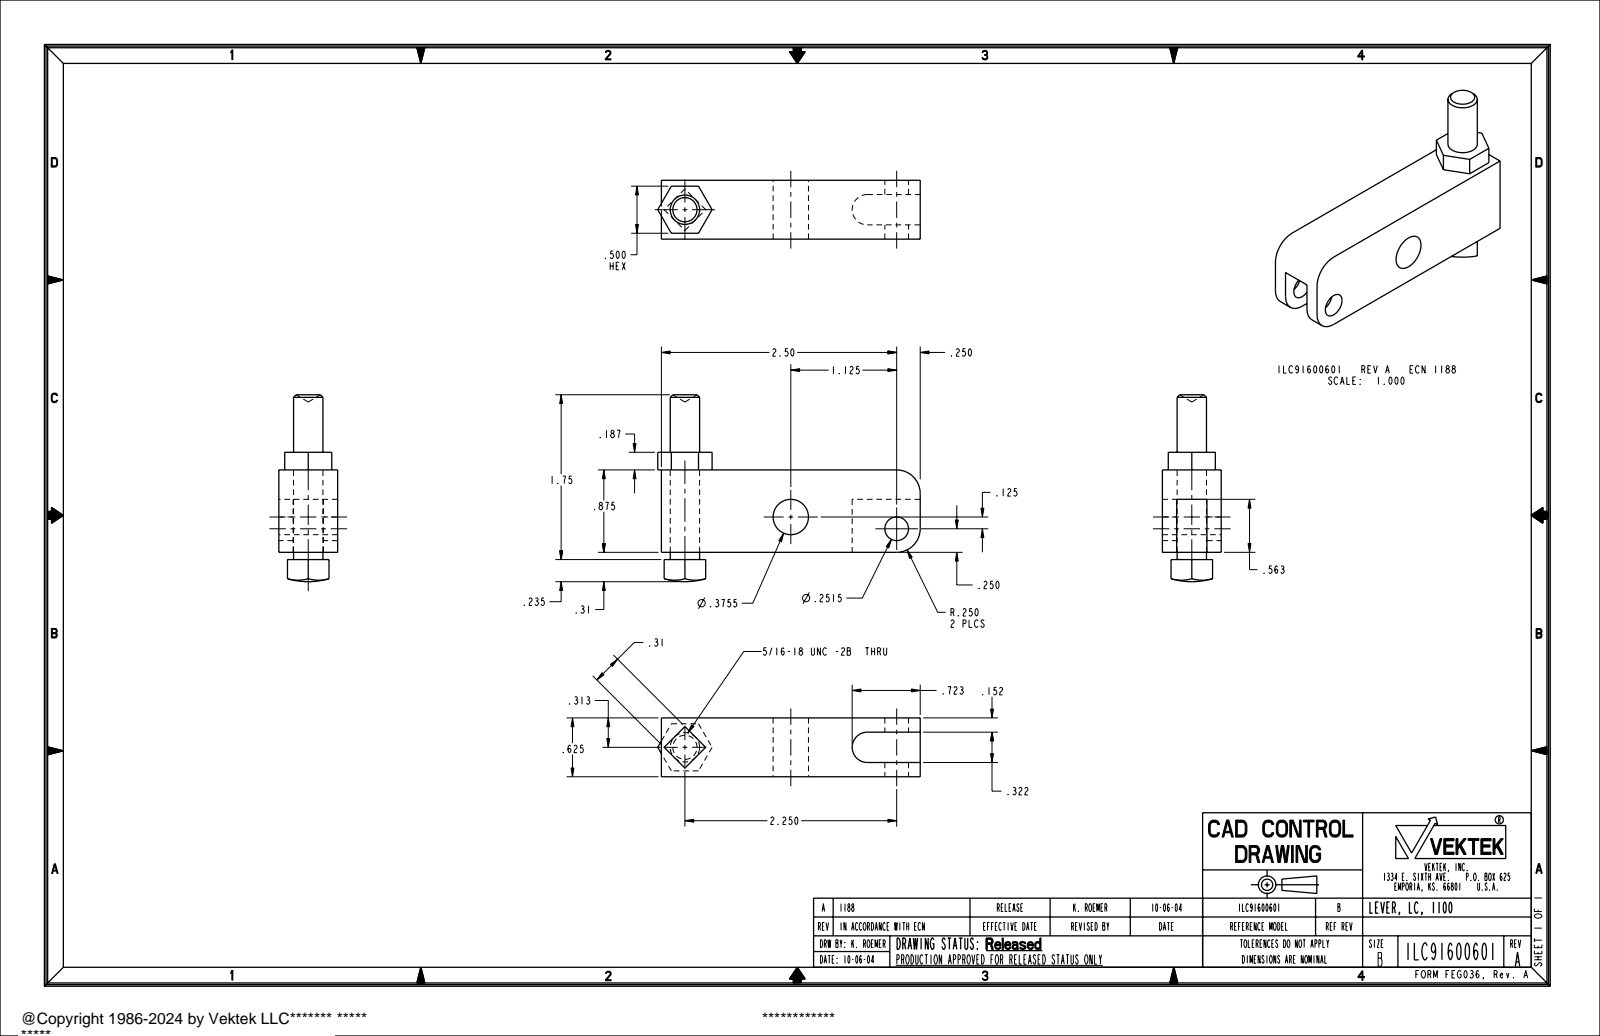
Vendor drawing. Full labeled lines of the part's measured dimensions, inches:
Part name (STEP PRODUCT): 91600601
STEP written by: PRO/ENGINEER BY PARAMETRIC TECHNOLOGY CORPORATION, 2004290 (CONFIG_CONTROL_DESIGN)
Units: inches
Bodies: 1 solid, 47 faces (25 planar, 16 cylindrical, 6 other)
Overall size (bounding box): 2.789 × 1.985 × 0.625
Volume: 1.396 in³ · Surface area: 12.62 in²
Round holes (diameter × count): ⌀0.251 ×1, ⌀0.376 ×1
Round bosses / shafts (diameter × count): ⌀0.312 ×1
Partial cylindrical surfaces — rounded edges, fillets, slot ends (radius × count): R0.25 ×2, R0.161 ×1
Main face-to-face distances: 0.625, 0.875, 0.152, 0.474, 0.312, 0.322, 0.563, 0.5, 1.062, 0.499
Hole centre spacings: 1.132
